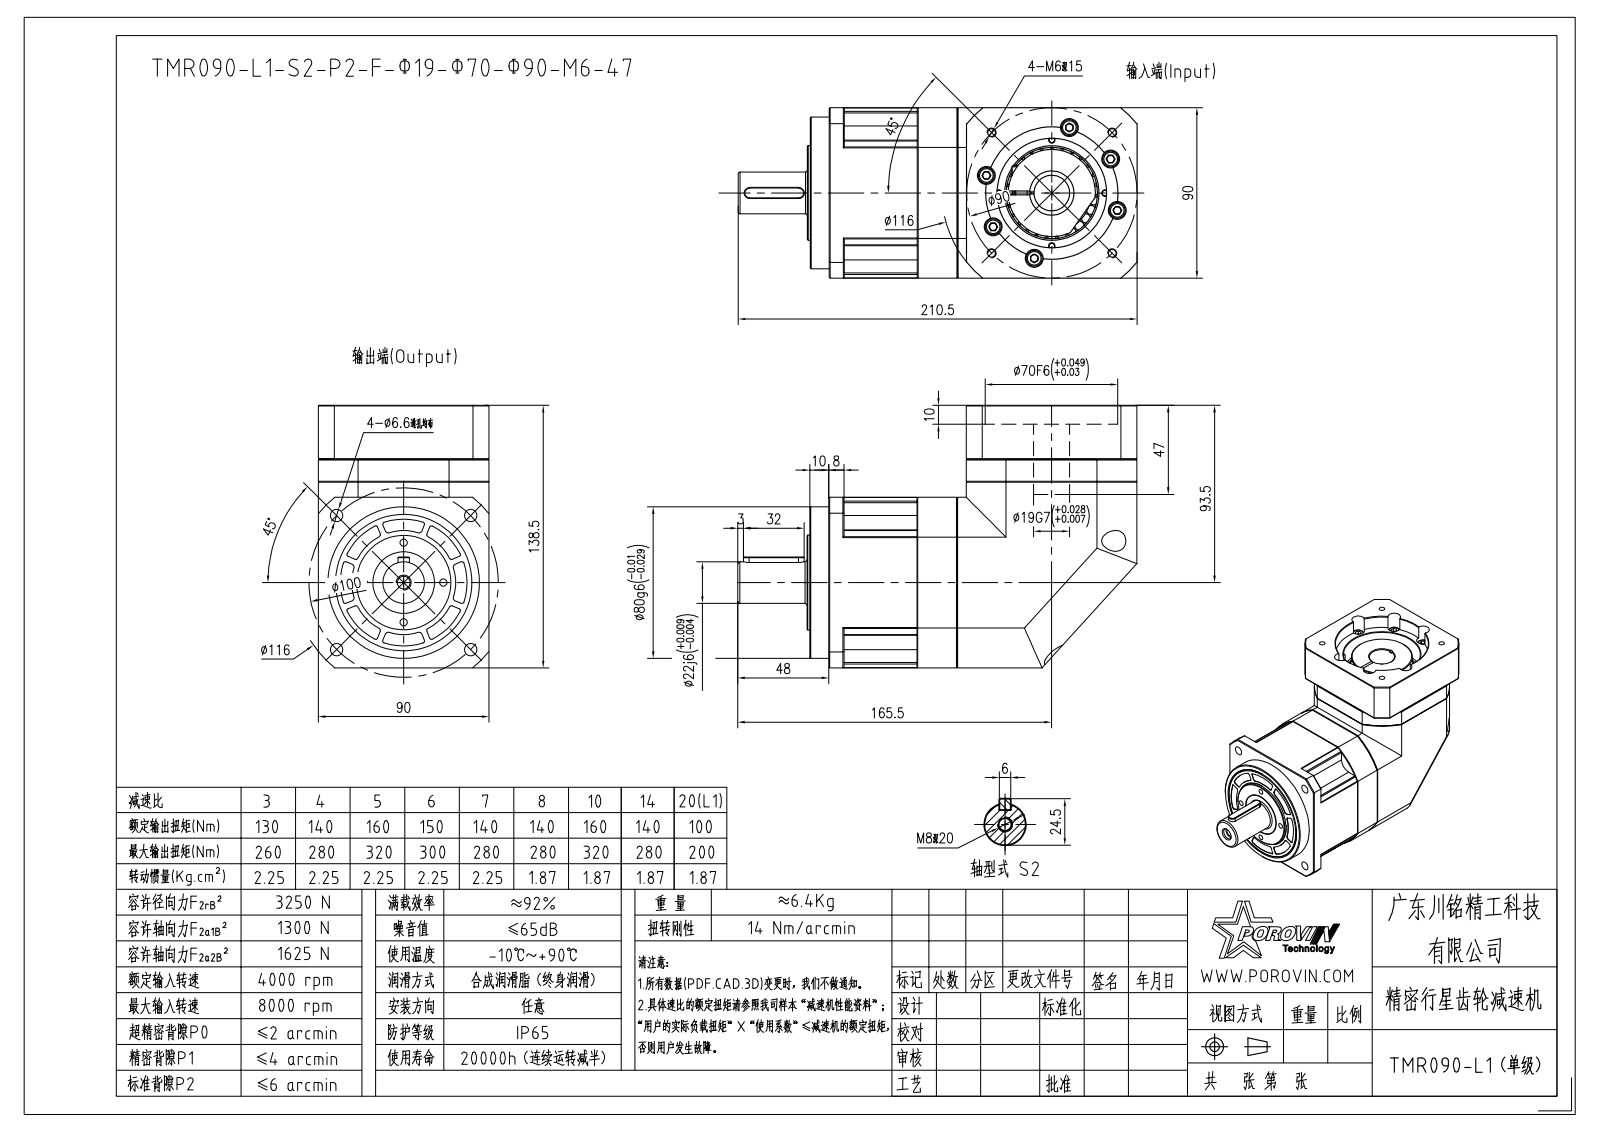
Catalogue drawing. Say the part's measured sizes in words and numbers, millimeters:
The part is named "HEXAGON_SOCKET_HEAD_CAP_S-13622; SPRING_LOCK_WASHERS--NORM-24193; SPRING_LOCK_WASHERS--NORMA-2869; HEXAGON_SOCKET_HEAD_CAP_SC-2921 (+8 more)". Its 3-D file was written by "CREO PARAMETRIC BY PTC INC, 2020053 (CONFIG_CONTROL_DESIGN)". It is 42 solids with 1283 faces: 512 planar, 545 cylindrical and 226 other. Overall it measures 210.5 by 138.5 by 90 millimeters. Its volume is 1 341 000 cubic millimeters and its surface area 208 187 square millimeters. Round holes: 12 of diameter 5.4, 12 of diameter 5.5, 12 of diameter 9.5, 7 of diameter 4.2, 5 of diameter 5, 5 of diameter 6.5, 4 of diameter 4, 4 of diameter 6.6, 4 of diameter 6.68, 4 of diameter 11, 1 of diameter 6.8, 1 of diameter 8.4. Round bosses or shafts: 12 of diameter 8.5, 12 of diameter 8, 12 of diameter 5, 4 of diameter 10, 4 of diameter 9.88, 4 of diameter 6, 1 of diameter 80, 1 of diameter 78. Partial cylindrical surfaces (rounded edges, fillets, slot ends): 92 of radius 1, 4 of radius 7.5, 3 of radius 51, 2 of radius 3, 2 of radius 58, 1 of radius 4, 1 of radius 5.25, 1 of radius 20.75. The main face-to-face distances are 90, 12, 21.3, 21.5, 10, 26, 110, 28.5, 98, 31.3. The hole center spacings are 35.75, 27.36, 38.16, 66.06, 66.53, 64.31, 80.07, 13.97.
